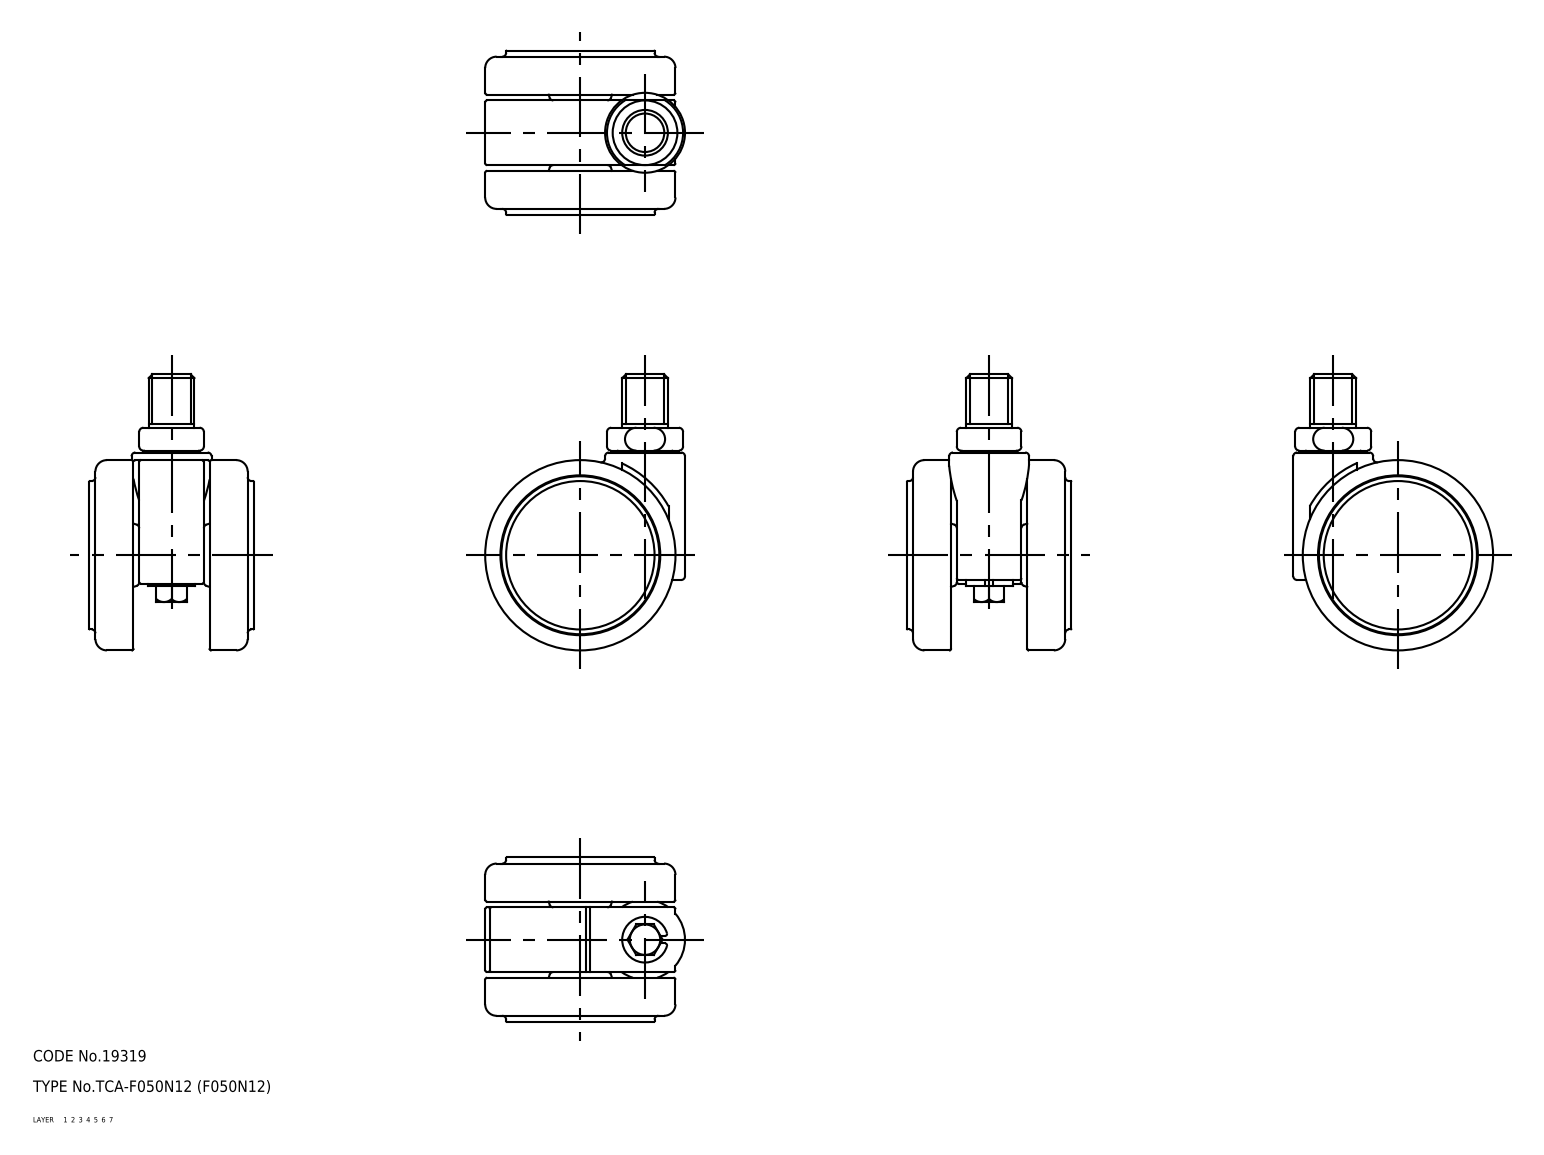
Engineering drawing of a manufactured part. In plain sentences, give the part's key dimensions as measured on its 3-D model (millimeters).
The part is named "67117955; 67117968; 67117981; 67117994". Its 3-D file was written by "CADfix (AUTOMOTIVE_DESIGN)". It is 4 solids with 131 faces: 0 planar, 0 cylindrical and 131 other. Overall it measures 72.5 by 52.5 by 43.2 millimeters. Its volume is 62 022 cubic millimeters and its surface area 21 432 square millimeters.
